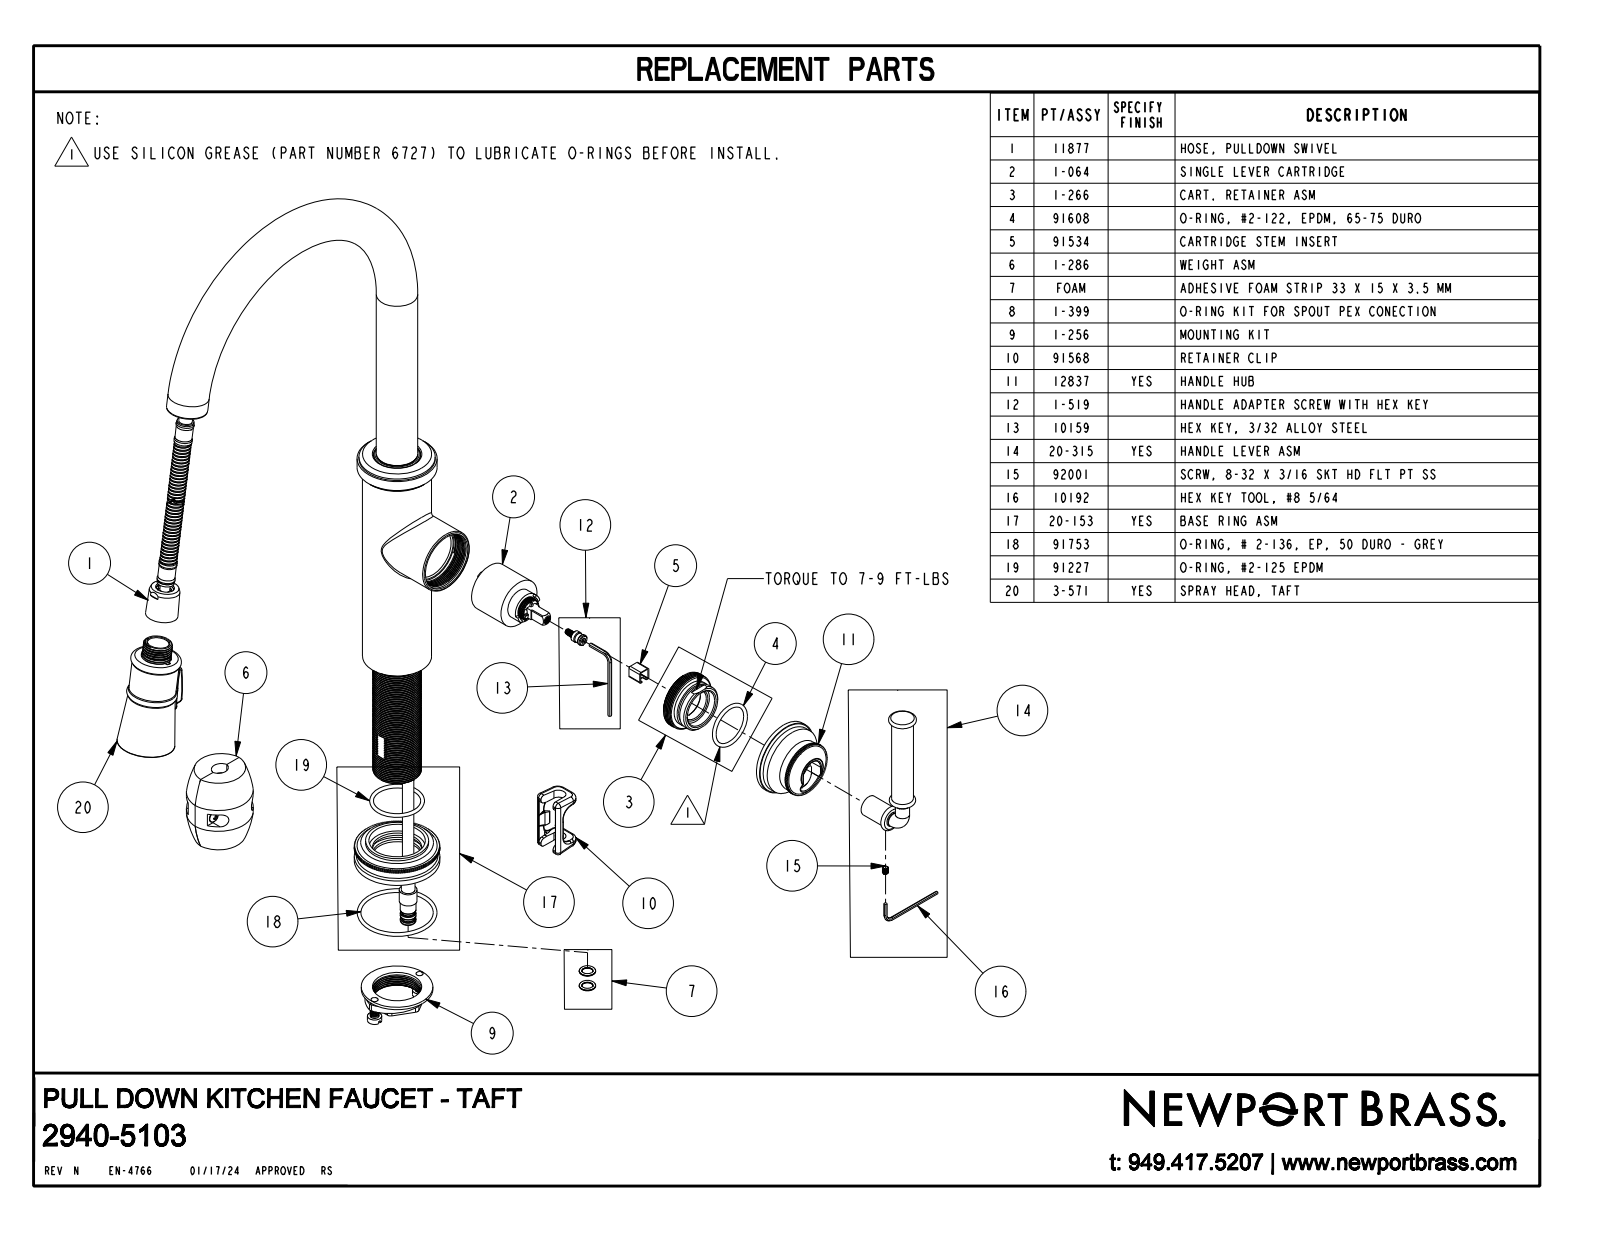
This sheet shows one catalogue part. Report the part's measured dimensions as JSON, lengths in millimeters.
{"part_name": "2940-5103", "step_written_by": "CREO PARAMETRIC BY PTC INC, 2018400 (CONFIG_CONTROL_DESIGN)", "units": "millimeters", "bodies": {"solids": 1, "faces": 995, "planar": 491, "cylindrical": 265, "other": 239}, "overall_size": [432.9, 266.6, 134.3], "volume_mm3": 815700, "surface_area_mm2": 100500, "round_holes": [[10.4, 1], [12.5, 1], [31.5, 1]], "round_bosses_or_shafts": [[53.3, 2], [9.9, 2], [59.7, 1], [57.2, 1], [55.9, 1], [49.3, 1], [48.3, 1], [45.7, 1]], "partial_cylinders_radius": [[1.5, 4], [3.7, 4], [0.5, 2], [2.5, 2], [8.6, 2], [19.7, 1], [71.1, 1]], "face_to_face_distances": [188.2, 2.5, 161.3, 163.8, 13, 175.3, 174.2, 14, 176.8, 184.4]}
